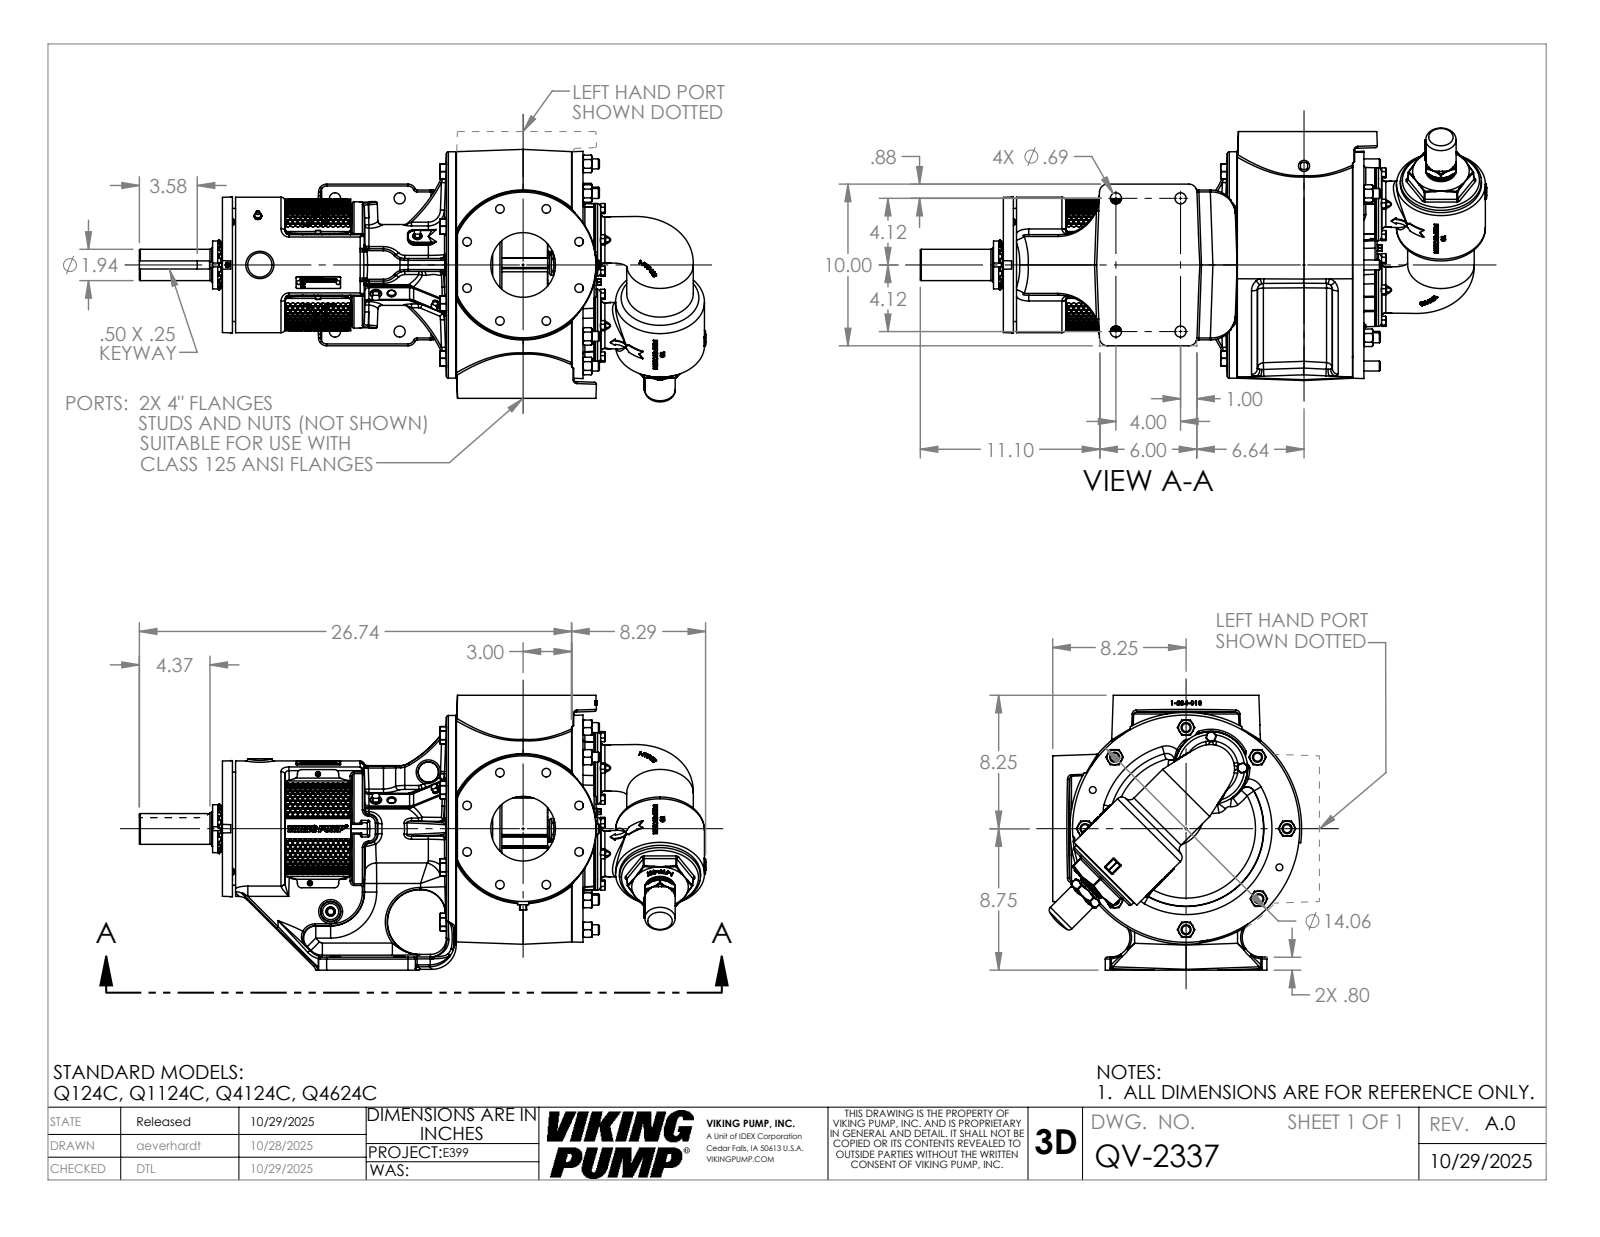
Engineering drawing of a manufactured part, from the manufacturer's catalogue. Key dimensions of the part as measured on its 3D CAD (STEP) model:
Part name (STEP PRODUCT): QV-2337
STEP written by: SolidWorks 2024 (AUTOMOTIVE_DESIGN)
Units: inches
Bodies: 1 solid, 4774 faces (1598 planar, 743 cylindrical, 2433 other)
Overall size (bounding box): 35.035 × 19.211 × 17.61
Volume: 2 246 in³ · Surface area: 2 327 in²
Round holes (diameter × count): ⌀0.266 ×8, ⌀0.406 ×8, ⌀0.41 ×8, ⌀1.157 ×8, ⌀0.25 ×6, ⌀0.531 ×4, ⌀0.688 ×4, ⌀0.159 ×2, ⌀0.313 ×2, ⌀0.422 ×2, ⌀0.453 ×1, ⌀2.157 ×1
Round bosses / shafts (diameter × count): ⌀0.617 ×24, ⌀0.625 ×15, ⌀0.375 ×6, ⌀0.375 ×4, ⌀0.312 ×4, ⌀0.437 ×3, ⌀4.5 ×2, ⌀14 ×1
Partial cylindrical surfaces — rounded edges, fillets, slot ends (radius × count): R0.12 ×68, R0.25 ×21, R0.06 ×20, R0.015 ×18, R0.092 ×18, R0.07 ×16, R0.75 ×14, R0.03 ×13
Main face-to-face distances: 17, 22.31, 1.25, 3.82, 18.49, 7.965, 4.145, 14.345, 20.81, 16.99
Hole centre spacings: 3.75, 2.079, 5.783, 2.713, 3.788, 5.423, 1.823, 3.133
